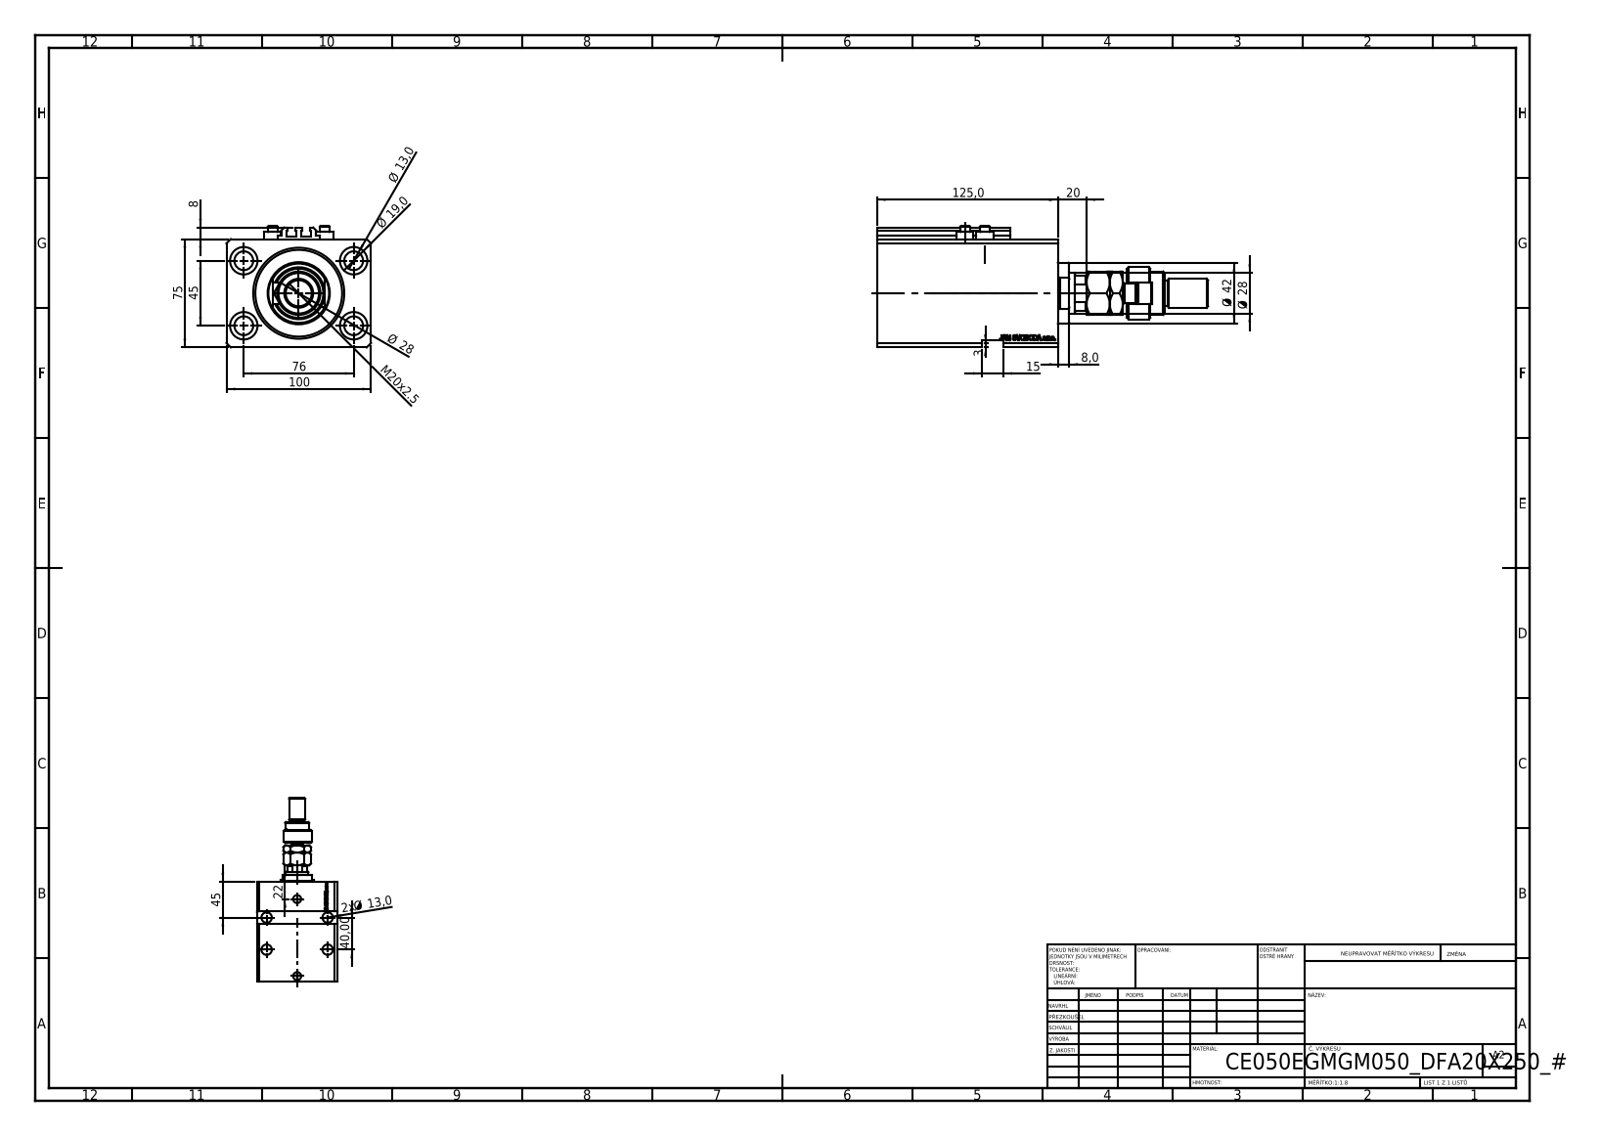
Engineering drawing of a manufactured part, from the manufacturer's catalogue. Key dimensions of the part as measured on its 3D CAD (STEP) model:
Part name (STEP PRODUCT): V250CE_VC_E; MFA; V250CE_C_VCP; ALLEN BOLT V250CE (+2 more)
STEP written by: SolidWorks 2019 (CONFIG_CONTROL_DESIGN)
Units: millimetres
Bodies: 10 solids, 1193 faces (563 planar, 159 cylindrical, 471 other)
Overall size (bounding box): 229 × 100 × 84
Volume: 817 731 mm³ · Surface area: 163 592 mm²
Round holes (diameter × count): ⌀13 ×8, ⌀1.25 ×4, ⌀4 ×4, ⌀19 ×4, ⌀10 ×2, ⌀13.16 ×2, ⌀20 ×2, ⌀18.5 ×1, ⌀28 ×1, ⌀50 ×1, ⌀63 ×1
Round bosses / shafts (diameter × count): ⌀11.6 ×4, ⌀7 ×4, ⌀42 ×1, ⌀36 ×1, ⌀30 ×1, ⌀22 ×1, ⌀20 ×1, ⌀18 ×1
Partial cylindrical surfaces — rounded edges, fillets, slot ends (radius × count): R0.2 ×10, R7.5 ×1, R12 ×1, R13.5 ×1
Main face-to-face distances: 75, 100, 20, 125, 11.9, 113.1, 105, 93.1, 70, 55
Hole centre spacings: 44.16, 76, 13.6, 20.72, 27.59, 29, 33.62, 36
